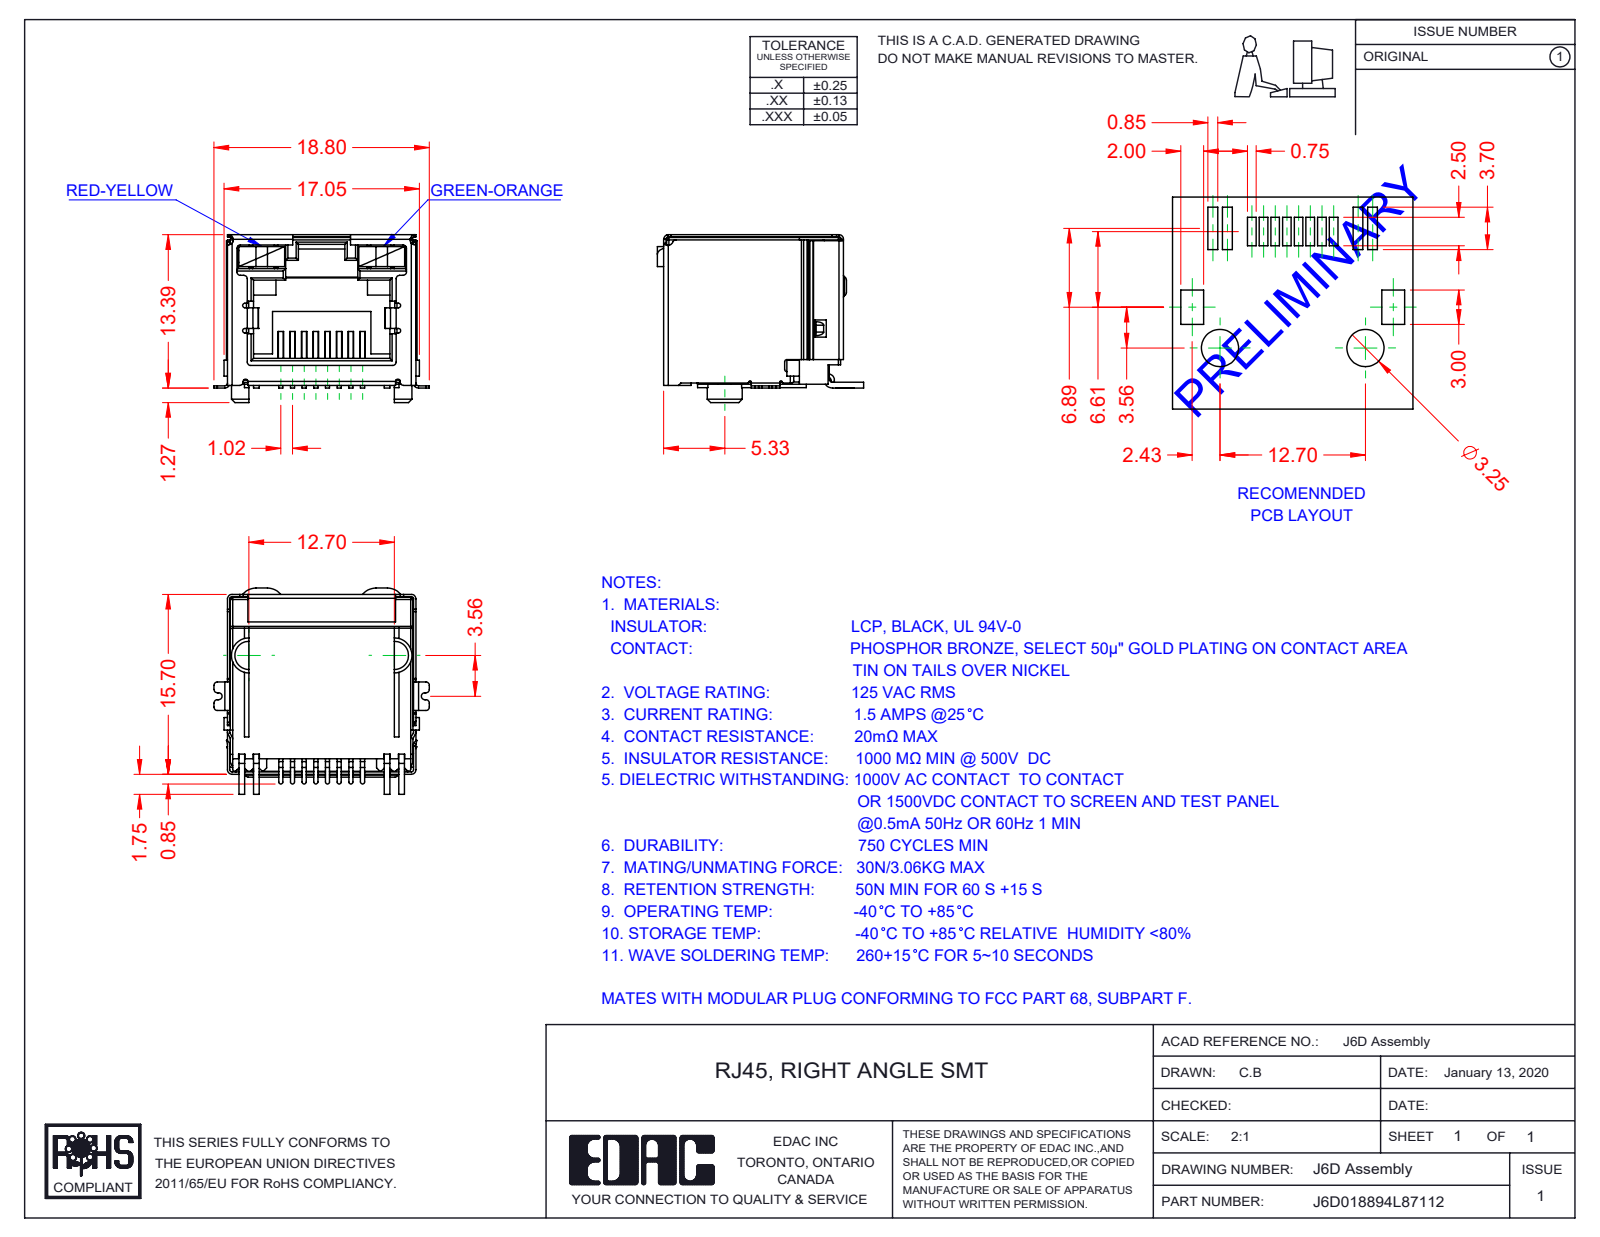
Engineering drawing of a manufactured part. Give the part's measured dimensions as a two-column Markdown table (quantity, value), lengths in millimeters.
| quantity | value |
| --- | --- |
| part name | 6D LED RH_7-Green-Orange; 6D LED LH_8-Red-Yellow; 6D Contacts; 6D Shield_LED - No EMI (+2 more) |
| STEP written by | SolidWorks 2016 (CONFIG_CONTROL_DESIGN) |
| units | millimeters |
| bodies | 12 solids, 899 faces (646 planar, 220 cylindrical, 33 other) |
| overall size | 18.8 × 18 × 14.65 |
| volume | 1 804 mm³ |
| surface area | 4 898 mm² |
| partial cylindrical surfaces (radius × count) | 0.3 × 39, 0.2 × 37, 0.4 × 16, 0.1 × 12, 0.15 × 8, 0.18 × 8, 0.5 × 6, 1.5 × 5 |
| main face-to-face distances | 16, 16.25, 16.2, 2.25, 1, 15.95, 16.05, 12.8, 0.45, 16.45 |
